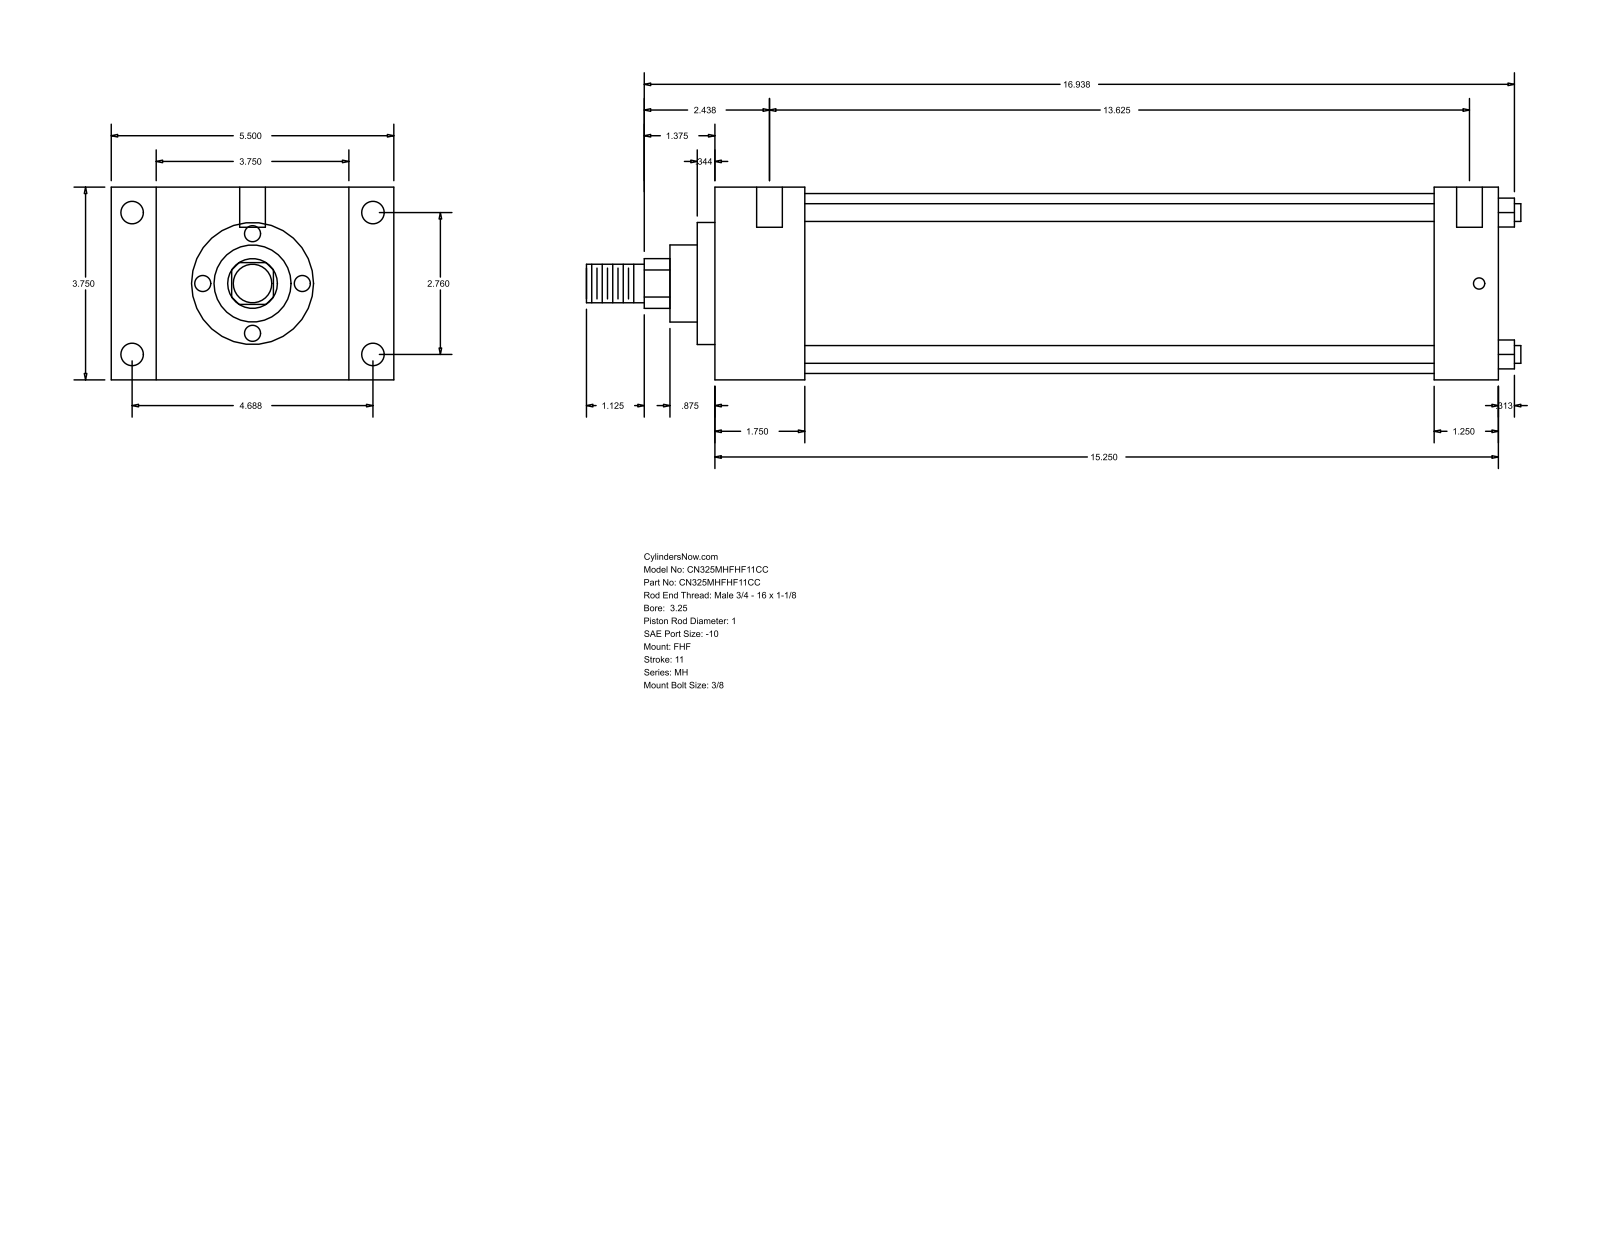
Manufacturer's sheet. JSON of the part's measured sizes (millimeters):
{"part_name": "MH_FHF__0325_1", "step_written_by": "GSSL Pune (CONFIG_CONTROL_DESIGN)", "units": "millimeters", "bodies": {"solids": 0, "faces": 90, "planar": 61, "cylindrical": 29, "other": 0}, "overall_size": [461.96, 139.7, 95.25], "round_holes": [[5.56, 4], [11.13, 4], [12.7, 2]], "round_bosses_or_shafts": [[8.76, 4], [88.9, 1], [60.33, 1], [38.1, 1], [25.4, 1], [19.05, 1]], "partial_cylinders_radius": [[12.29, 1]], "face_to_face_distances": [95.24, 387.35, 44.46, 342.89, 22.23, 117.47, 139.7, 355.6, 311.14, 31.75], "hole_center_spacings": [70.1, 119.06, 138.16, 352.42, 1.58, 4.76, 346.08, 347.66]}
